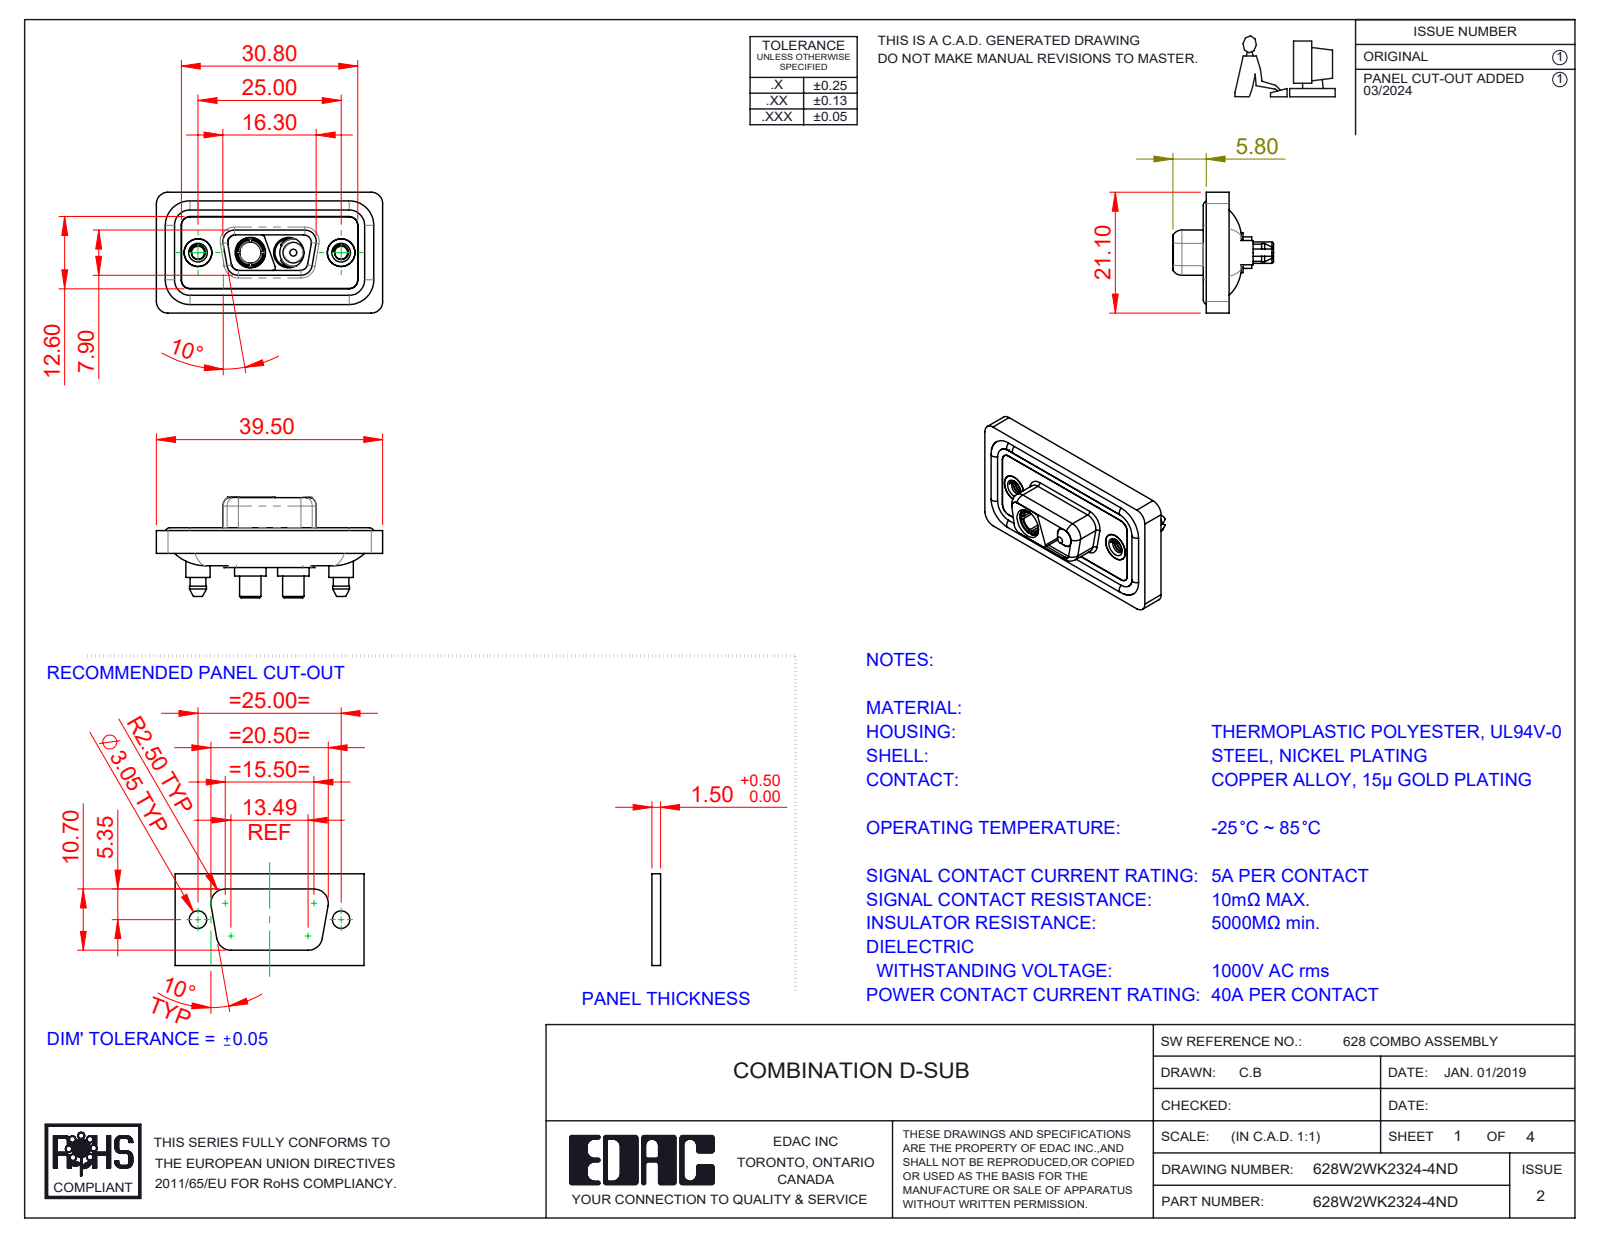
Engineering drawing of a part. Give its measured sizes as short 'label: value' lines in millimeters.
name: 628Combo Shell Front_09 Contacts; 628Combo Threaded Boardlock_D; 628Combo Housing_2WK2; Power Socket_40A S (+4 more)
written by: SolidWorks 2023 (CONFIG_CONTROL_DESIGN)
unit: mm
bodies: 11 solids, 566 faces (160 planar, 279 cylindrical, 127 other)
size: 39.5 × 21.1 × 17.55
volume: 4 775 mm³; area: 7 705 mm²
holes: 4× ⌀4.85, 2× ⌀2.26, 2× ⌀4, 2× ⌀4.05, 2× ⌀5, 2× ⌀5.3, 1× ⌀3.7
bosses: 4× ⌀1.6, 2× ⌀5.5, 2× ⌀5.4, 2× ⌀5.2, 2× ⌀4.95, 2× ⌀4.8, 2× ⌀4.75, 2× ⌀4.25
rounds: 24× R1.5, 18× R2, 10× R1.6, 8× R1.35, 6× R0.5, 4× R0.25, 4× R0.6, 4× R0.65
face distances: 0.4, 1.1, 2.9, 1.6, 0.5, 1.8, 5.65, 4, 1.5, 5.35
hole spacings: 9.14, 15.86, 6.72, 25
